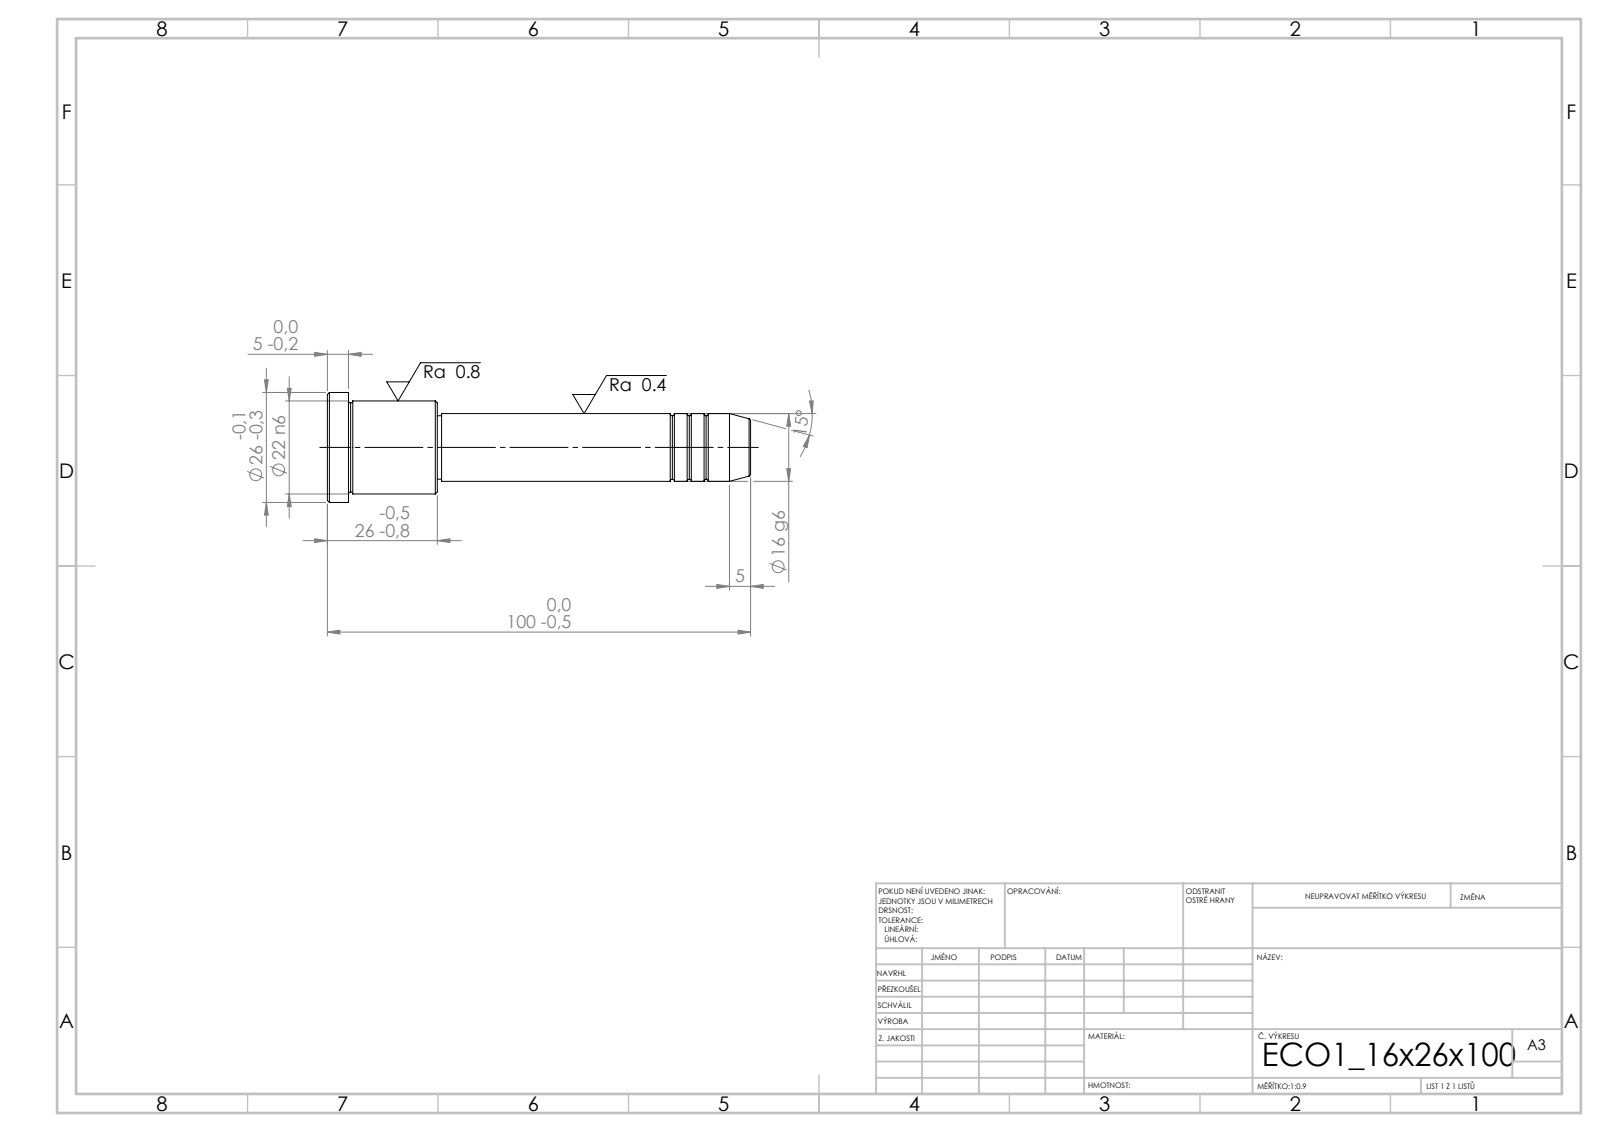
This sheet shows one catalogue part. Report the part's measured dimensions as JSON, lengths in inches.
{"step_written_by": "SolidWorks 2019 (CONFIG_CONTROL_DESIGN)", "units": "inches", "bodies": {"solids": 1, "faces": 43, "planar": 5, "cylindrical": 14, "other": 24}, "overall_size": [3.937, 1.024, 1.024], "volume_in3": 1.54, "surface_area_in2": 10.35, "round_bosses_or_shafts": [[1.024, 1], [0.866, 1], [0.63, 1], [0.591, 1]], "face_to_face_distances": [1.024, 0.827, 0.197, 2.913, 3.74, 3.937, 2.874, 0.039, 0.866, 1.063]}
